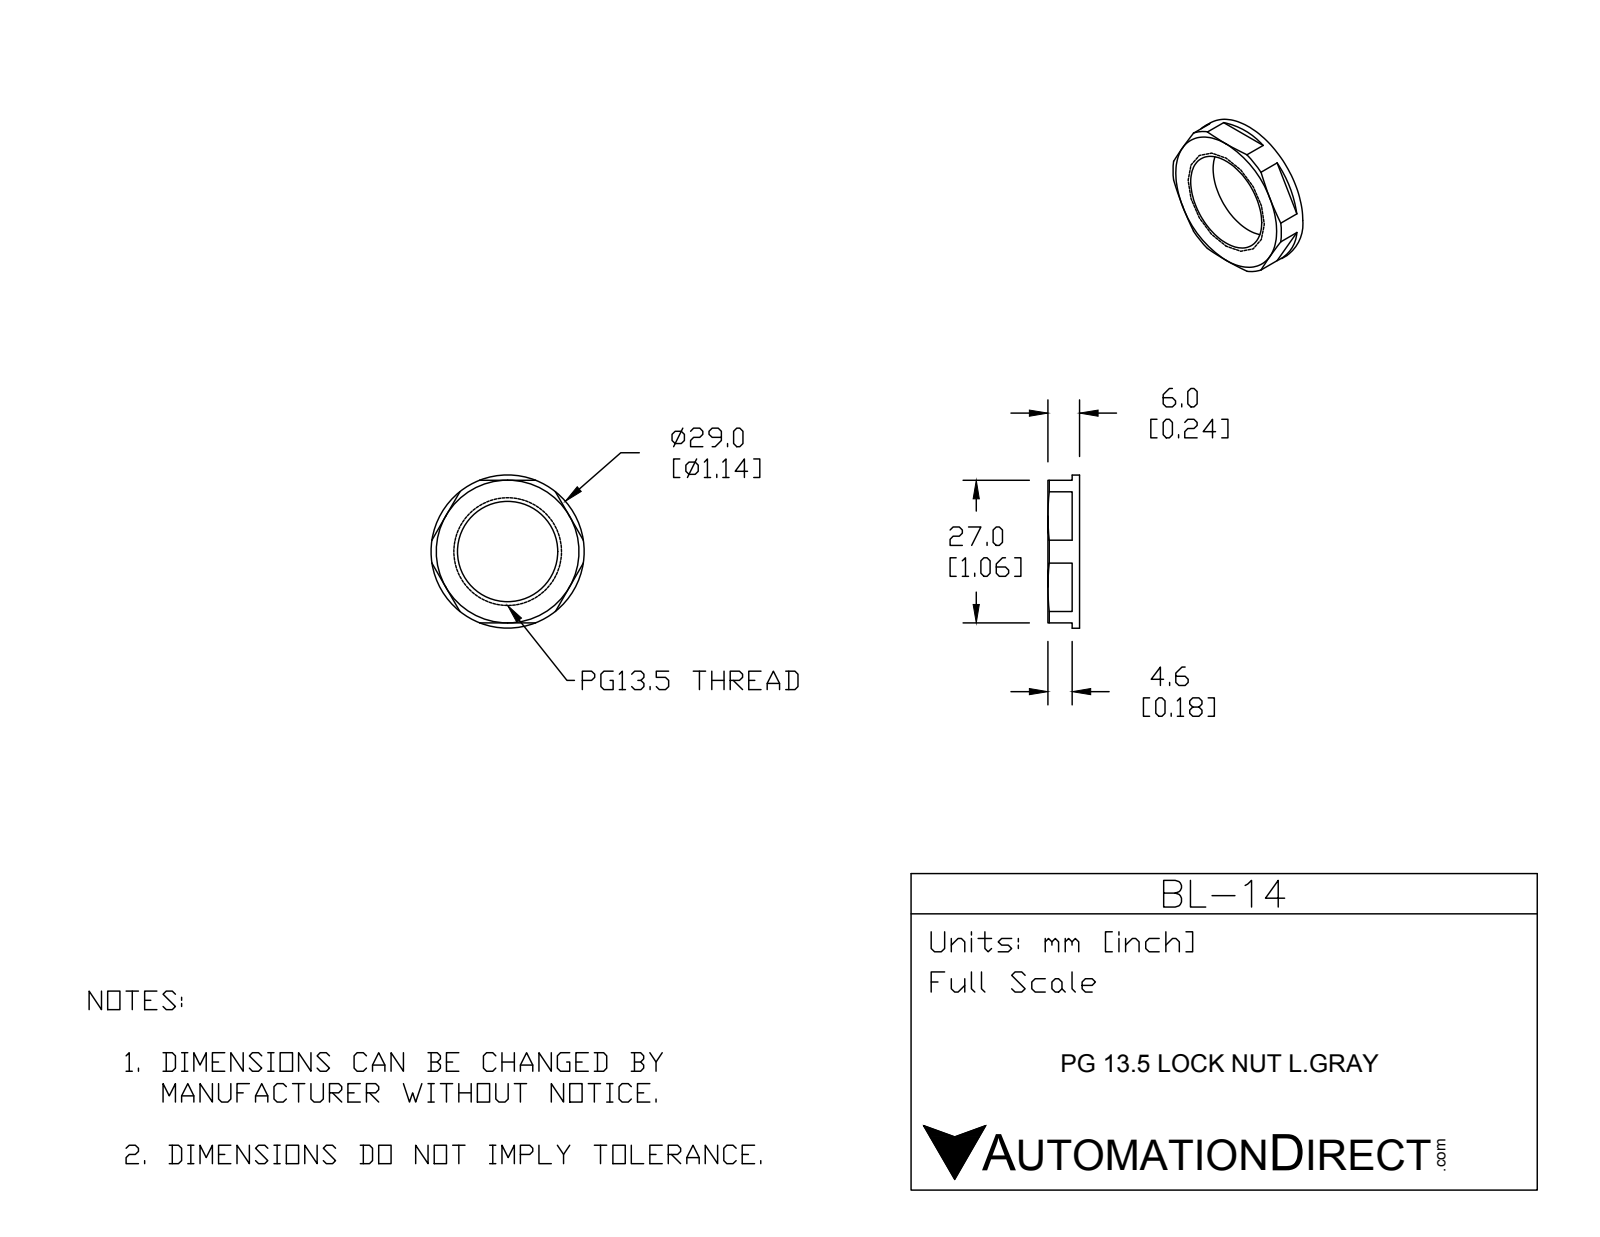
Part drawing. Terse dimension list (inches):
name: BL-14
written by: SolidWorks 2015 (CONFIG_CONTROL_DESIGN)
unit: in
bodies: 1 solid, 33 faces (17 planar, 10 cylindrical, 6 other)
size: 1.142 × 1.142 × 0.236
volume: 0.126 in³; area: 2.55 in²
holes: 3× ⌀0.059, 1× ⌀0.748
bosses: 1× ⌀1.142
face distances: 0.236, 1.063, 0.055, 0.181, 0.043, 0.224
hole spacings: 0.514, 0.89, 0.89
